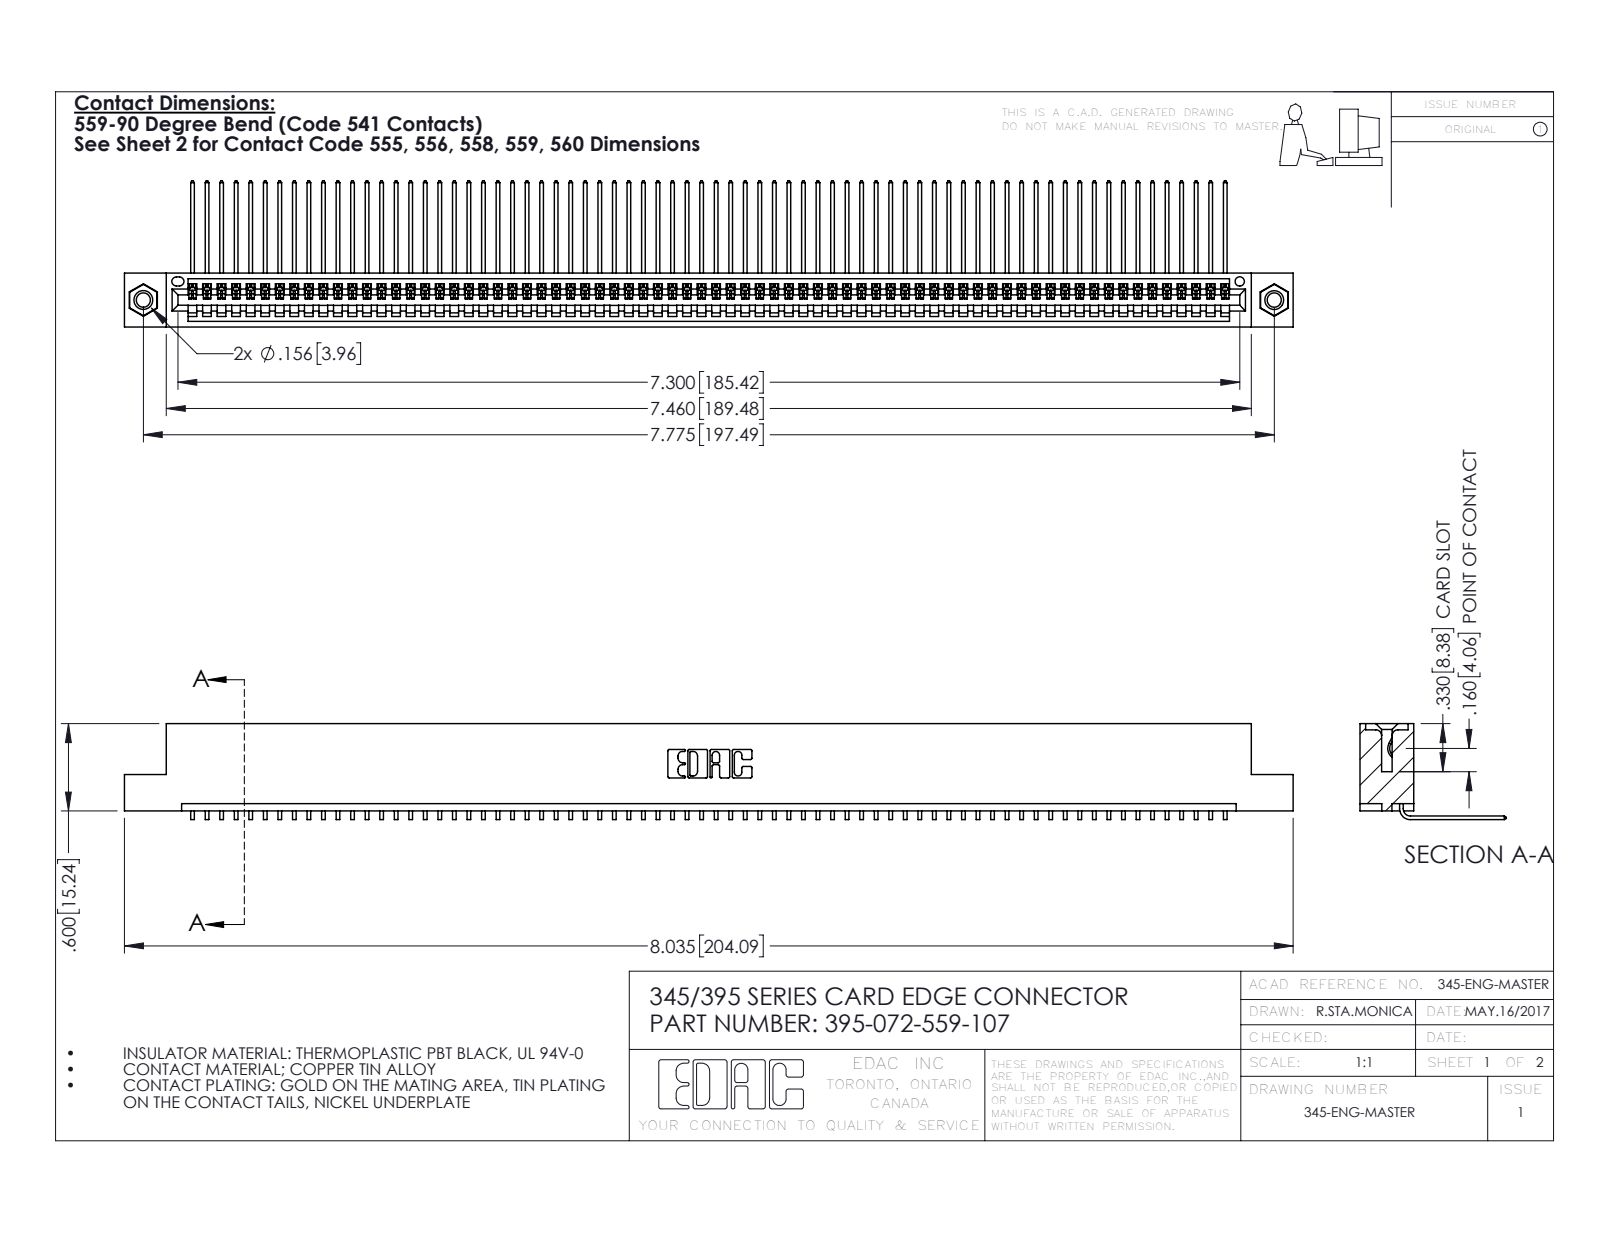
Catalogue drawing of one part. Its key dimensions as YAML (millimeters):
part_name: "345-292-001_558 559 Tail - 1; 345-250-001_345-250-005-103; 345 Part_Flush Mounting Lugs - 0.156 Dia-TI; 395-072-559-107"
step_written_by: "SolidWorks 2016 (CONFIG_CONTROL_DESIGN)"
units: millimeters
bodies: {solids: 75, faces: 4506, planar: 3136, cylindrical: 1354, other: 16}
overall_size: [204.1, 25.5, 16.7]
volume: 19860
surface_area: 28240
round_holes:
  - {diameter: 2.5, count: 2}
  - {diameter: 3.2, count: 2}
  - {diameter: 4, count: 2}
  - {diameter: 1.6, count: 1}
round_bosses_or_shafts:
  - {diameter: 3.9, count: 2}
partial_cylinders:
  - {radius: 0.2, count: 144}
  - {radius: 0.3, count: 22}
  - {radius: 0.2, count: 6}
  - {radius: 0.8, count: 6}
  - {radius: 0.7, count: 3}
  - {radius: 0.8, count: 2}
  - {radius: 1, count: 2}
  - {radius: 0.4, count: 1}
face_to_face_distances: [1.8, 7.6, 9.4, 5.1, 2.5, 6.9, 0.6, 5.7, 3.8, 1.8]
hole_center_spacings: [6.9, 191.5, 197.5]
